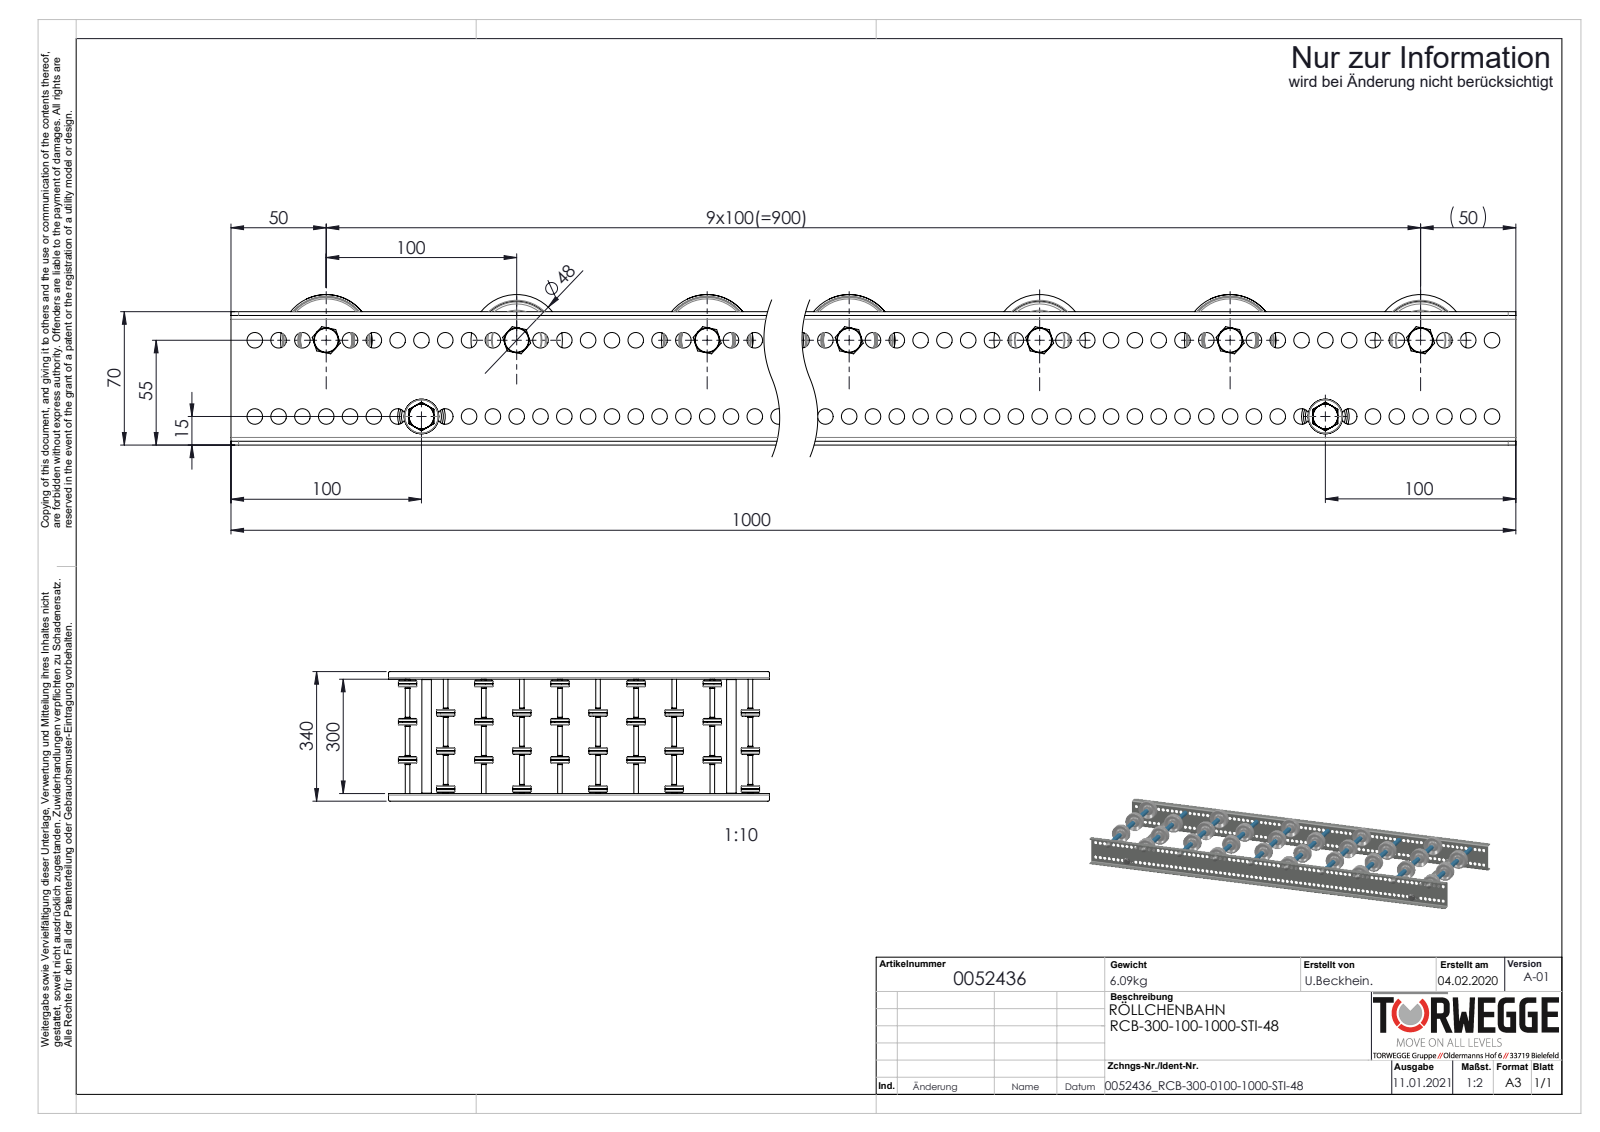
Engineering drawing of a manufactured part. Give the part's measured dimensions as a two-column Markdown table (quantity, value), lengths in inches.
| quantity | value |
| --- | --- |
| part name | Röllchenachse-für-Konfiguration_EL300 Stahl; K0011528_2200-48-8; Traversen_KFG_L300; Profil_LRB-20x70x20x2_KFG_S100200_U-PROFIL-20-70-20-2-LRB-L=1000 (+5 more) |
| STEP written by | SolidWorks 2020 (AUTOMOTIVE_DESIGN) |
| units | inches |
| bodies | 132 solids, 4132 faces (840 planar, 1688 cylindrical, 1604 other) |
| overall size | 39.37 × 13.386 × 3.11 |
| volume | 85.31 in³ |
| surface area | 1 750 in² |
| round holes (diameter × count) | 0.323 × 158, 0.262 × 10, 0.315 × 10, 0.38 × 10, 0.591 × 10, 1.614 × 10, 0.268 × 2, 0.827 × 2 |
| round bosses / shafts (diameter × count) | 1.89 × 10, 0.512 × 10, 0.492 × 10, 0.488 × 10, 0.472 × 10, 0.453 × 10, 0.984 × 2, 0.315 × 2 |
| partial cylindrical surfaces (radius × count) | 0.157 × 8, 0.079 × 4 |
| main face-to-face distances | 0.079, 11.89, 3.937, 2.677, 11.969, 11.811, 2.992, 0.472, 3.465, 7.874 |
| hole center spacings | 0.492, 0.984, 1.476, 1.969, 2.461, 2.953, 3.445, 3.937 |
